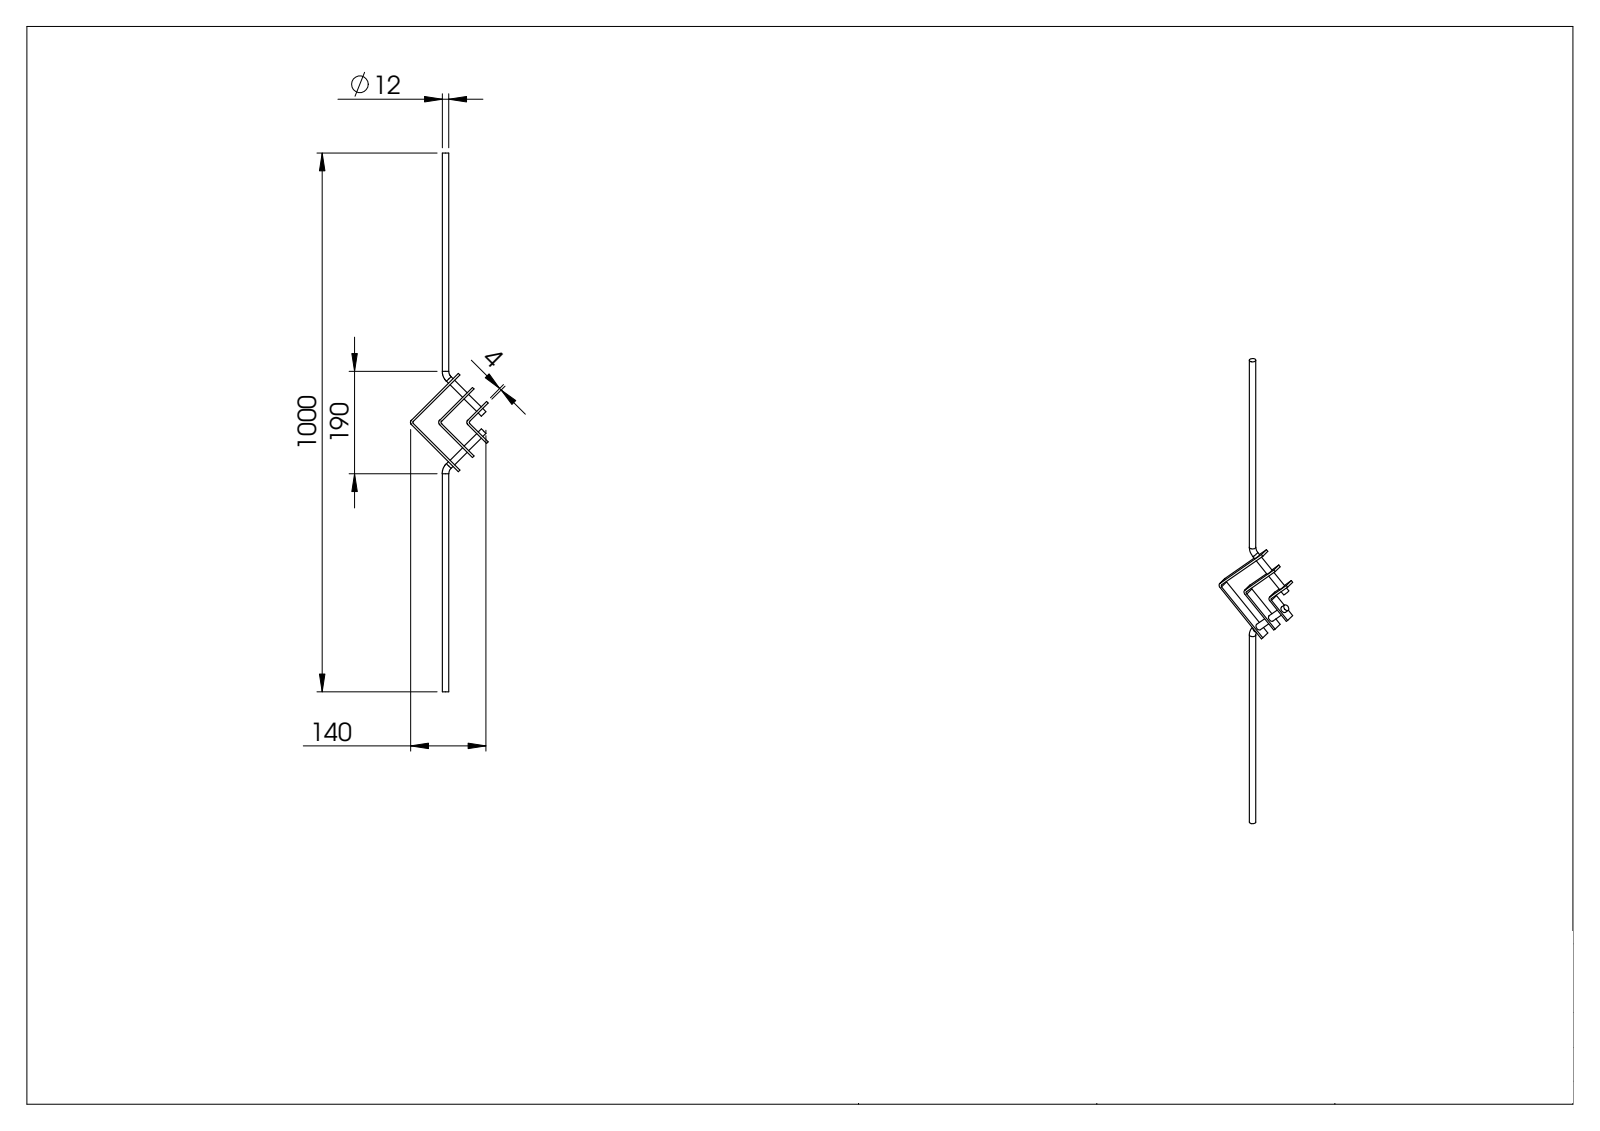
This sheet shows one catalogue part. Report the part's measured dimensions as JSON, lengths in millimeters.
{"part_name": "56304-240", "step_written_by": "SolidWorks 2015 (CONFIG_CONTROL_DESIGN)", "units": "millimeters", "bodies": {"solids": 1, "faces": 171, "planar": 93, "cylindrical": 26, "other": 52}, "overall_size": [1000, 143.89, 20], "volume_mm3": 156036, "surface_area_mm2": 62986, "round_bosses_or_shafts": [[12, 3]], "partial_cylinders_radius": [[2.99, 2], [5.97, 2], [3, 1], [6, 1]], "face_to_face_distances": [4, 36.99, 40.99, 32.99, 73.99, 37, 20, 69.99, 33, 77.98]}
